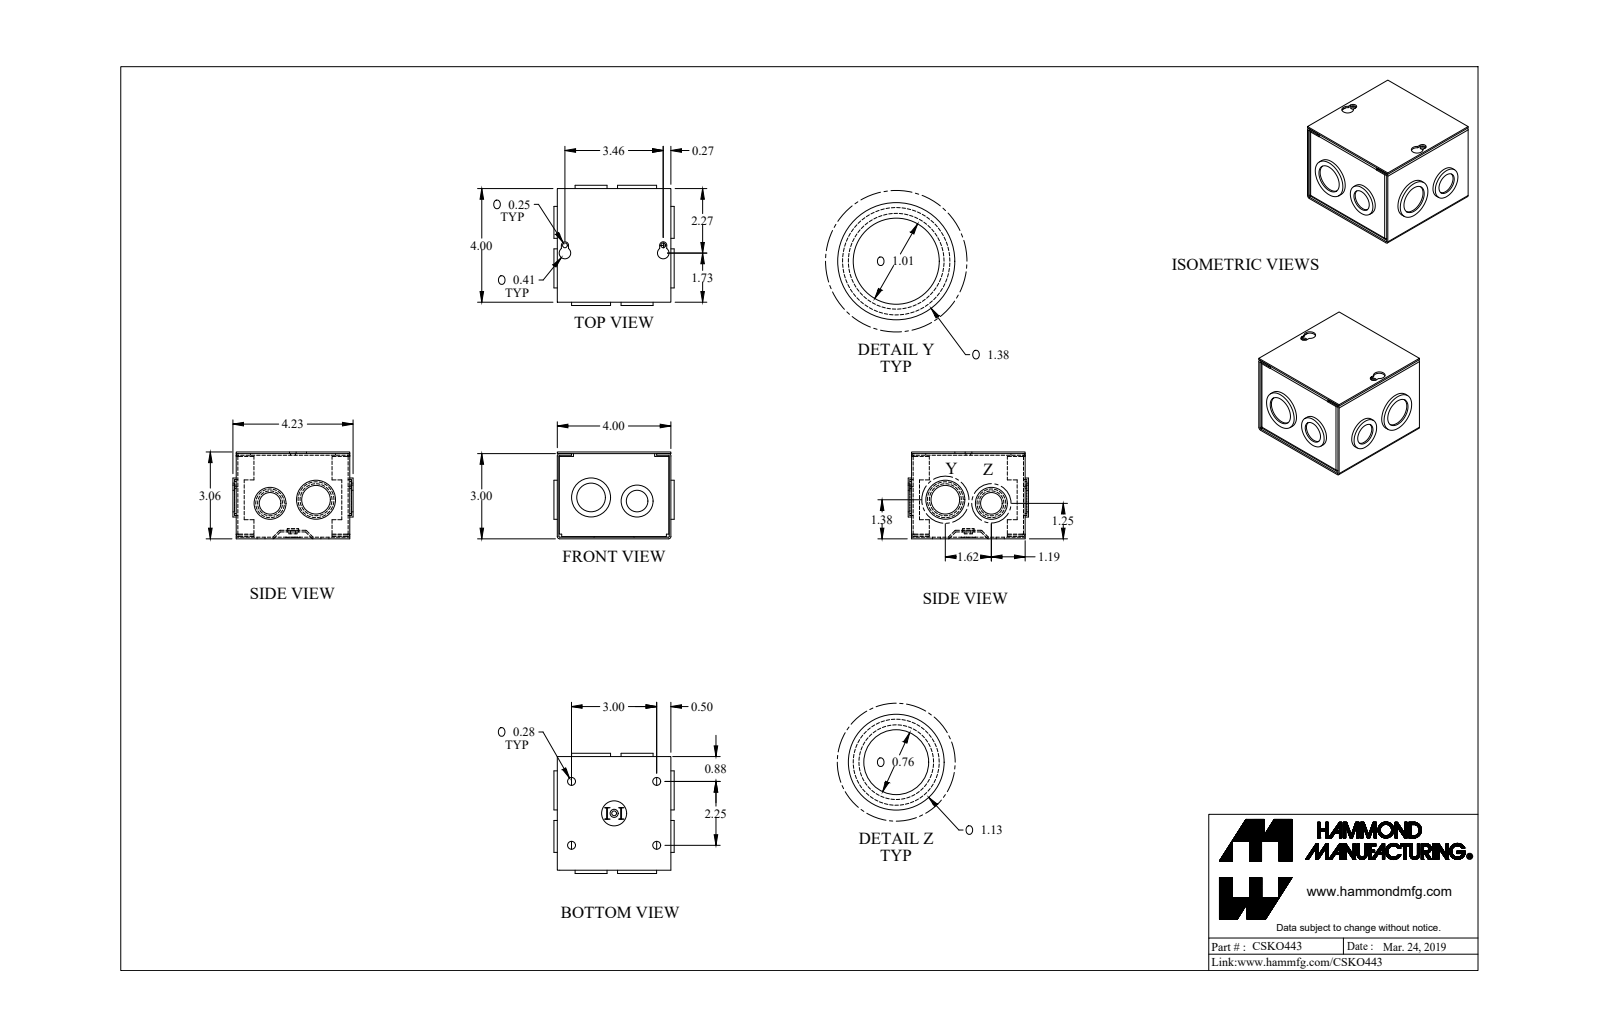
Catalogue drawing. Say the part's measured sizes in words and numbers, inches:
The part is named "CSKO443_Default". Its 3-D file was written by "SolidWorks 2019 (CONFIG_CONTROL_DESIGN)". It is 4 solids with 301 faces: 169 planar, 124 cylindrical and 8 other. Overall it measures 4.234 by 4.234 by 3.057 inches. Its volume is 5.48 cubic inches and its surface area 197.6 square inches. Round holes: 6 of diameter 1.011, 4 of diameter 0.281, 3 of diameter 0.17, 3 of diameter 0.761, 3 of diameter 1.261, 1 of diameter 0.5. Round bosses or shafts: 4 of diameter 1.125, 3 of diameter 0.875, 2 of diameter 1.375, 2 of diameter 1.125, 1 of diameter 1.375, 1 of diameter 0.875, 1 of diameter 0.492, 1 of diameter 0.284. Partial cylindrical surfaces (rounded edges, fillets, slot ends): 12 of radius 0.029, 12 of radius 0.086, 8 of radius 0.057, 2 of radius 0.125, 2 of radius 0.203. The main face-to-face distances are 0.057, 3.943, 3, 4, 2.943, 3.886, 3.057, 0.114, 0.08, 2.863. The hole center spacings are 1.148, 1.875, 3.42, 1.624, 0.125, 1.125, 1.62, 1.73.
